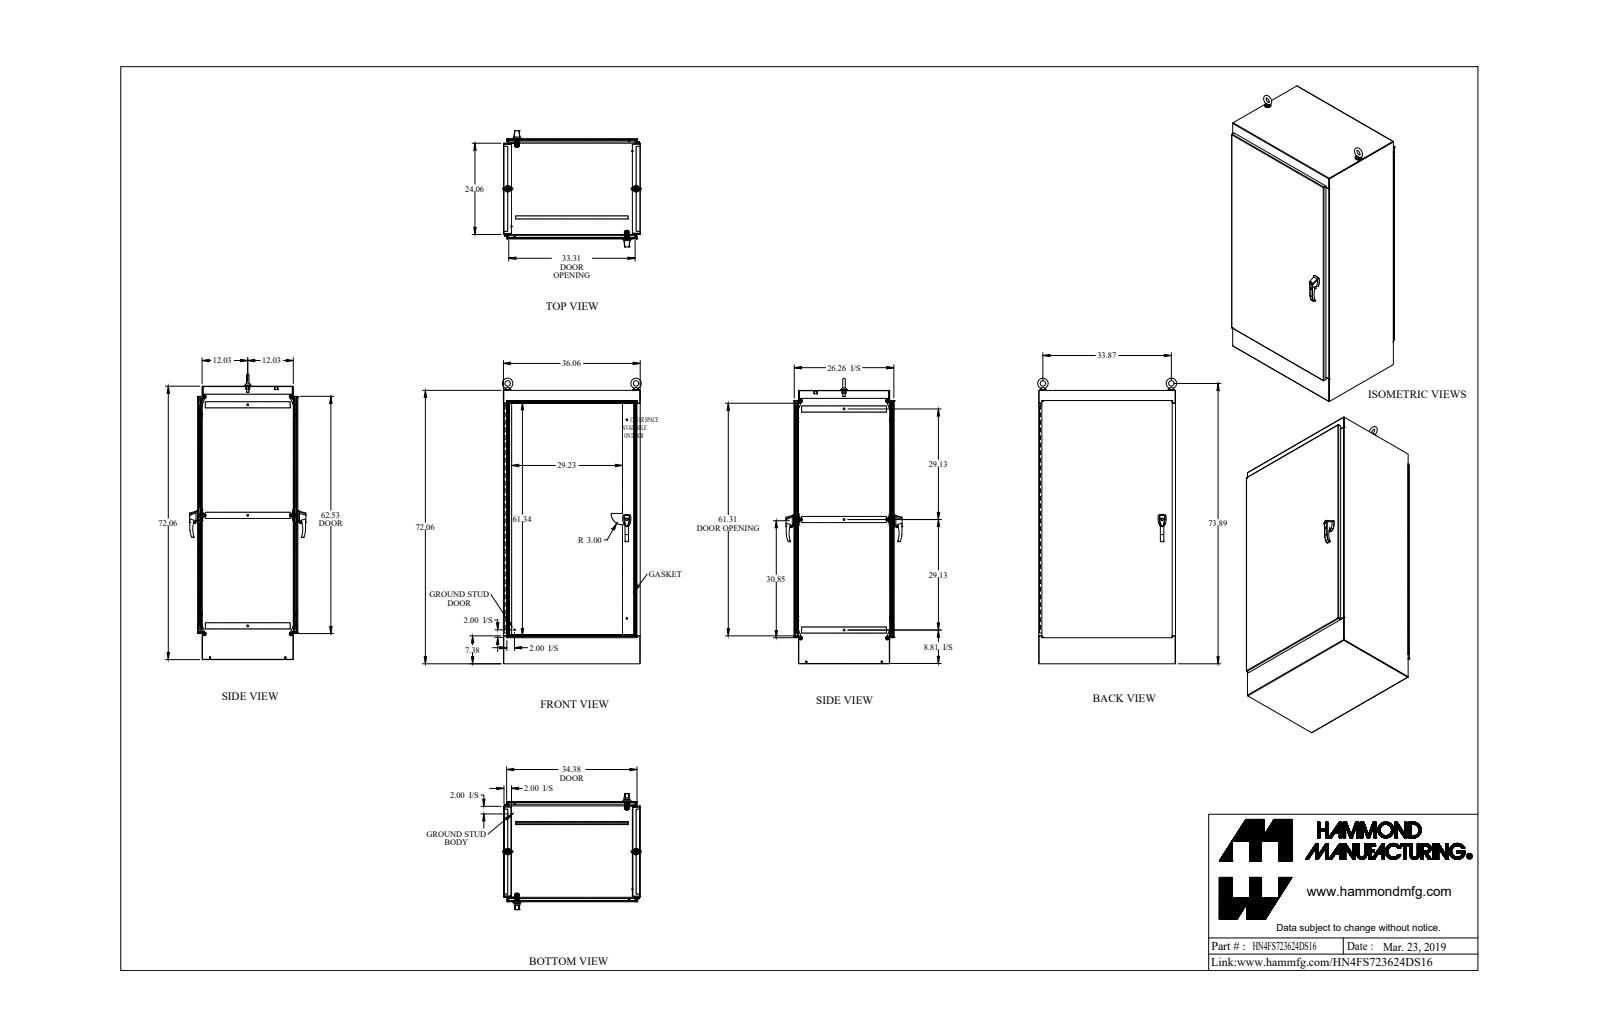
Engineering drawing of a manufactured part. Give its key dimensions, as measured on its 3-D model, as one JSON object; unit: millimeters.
{"part_name": "HN4FS723624DS16", "step_written_by": "SolidWorks 2018 (AUTOMOTIVE_DESIGN)", "units": "millimeters", "bodies": {"solids": 89, "faces": 3217, "planar": 1448, "cylindrical": 1501, "other": 268}, "overall_size": [1917.4, 929.7, 778.9], "volume_mm3": 20810000, "surface_area_mm2": 17280000, "round_holes": [[7.7, 20], [8.9, 8], [6.4, 4], [6.5, 4], [7.1, 4], [7.1, 4], [8, 4], [9.9, 4], [10.5, 4], [12.7, 3], [2.8, 2], [4.4, 2]], "round_bosses_or_shafts": [[25.4, 4], [19.1, 4], [16, 4], [15.9, 4], [11.2, 4], [9.4, 4], [8, 4], [7.1, 4]], "partial_cylinders_radius": [[3.2, 44], [1.1, 42], [3.5, 36], [0.5, 32], [1.2, 26], [3.6, 26], [12.7, 26], [1.5, 21]], "face_to_face_distances": [2.4, 669, 913.5, 666.6, 671.4, 30.1, 638.9, 911.1, 915.9, 1827.9], "hole_center_spacings": [152.4, 884.6, 304.8, 923.1, 457.2, 984, 609.6, 1063.4]}
